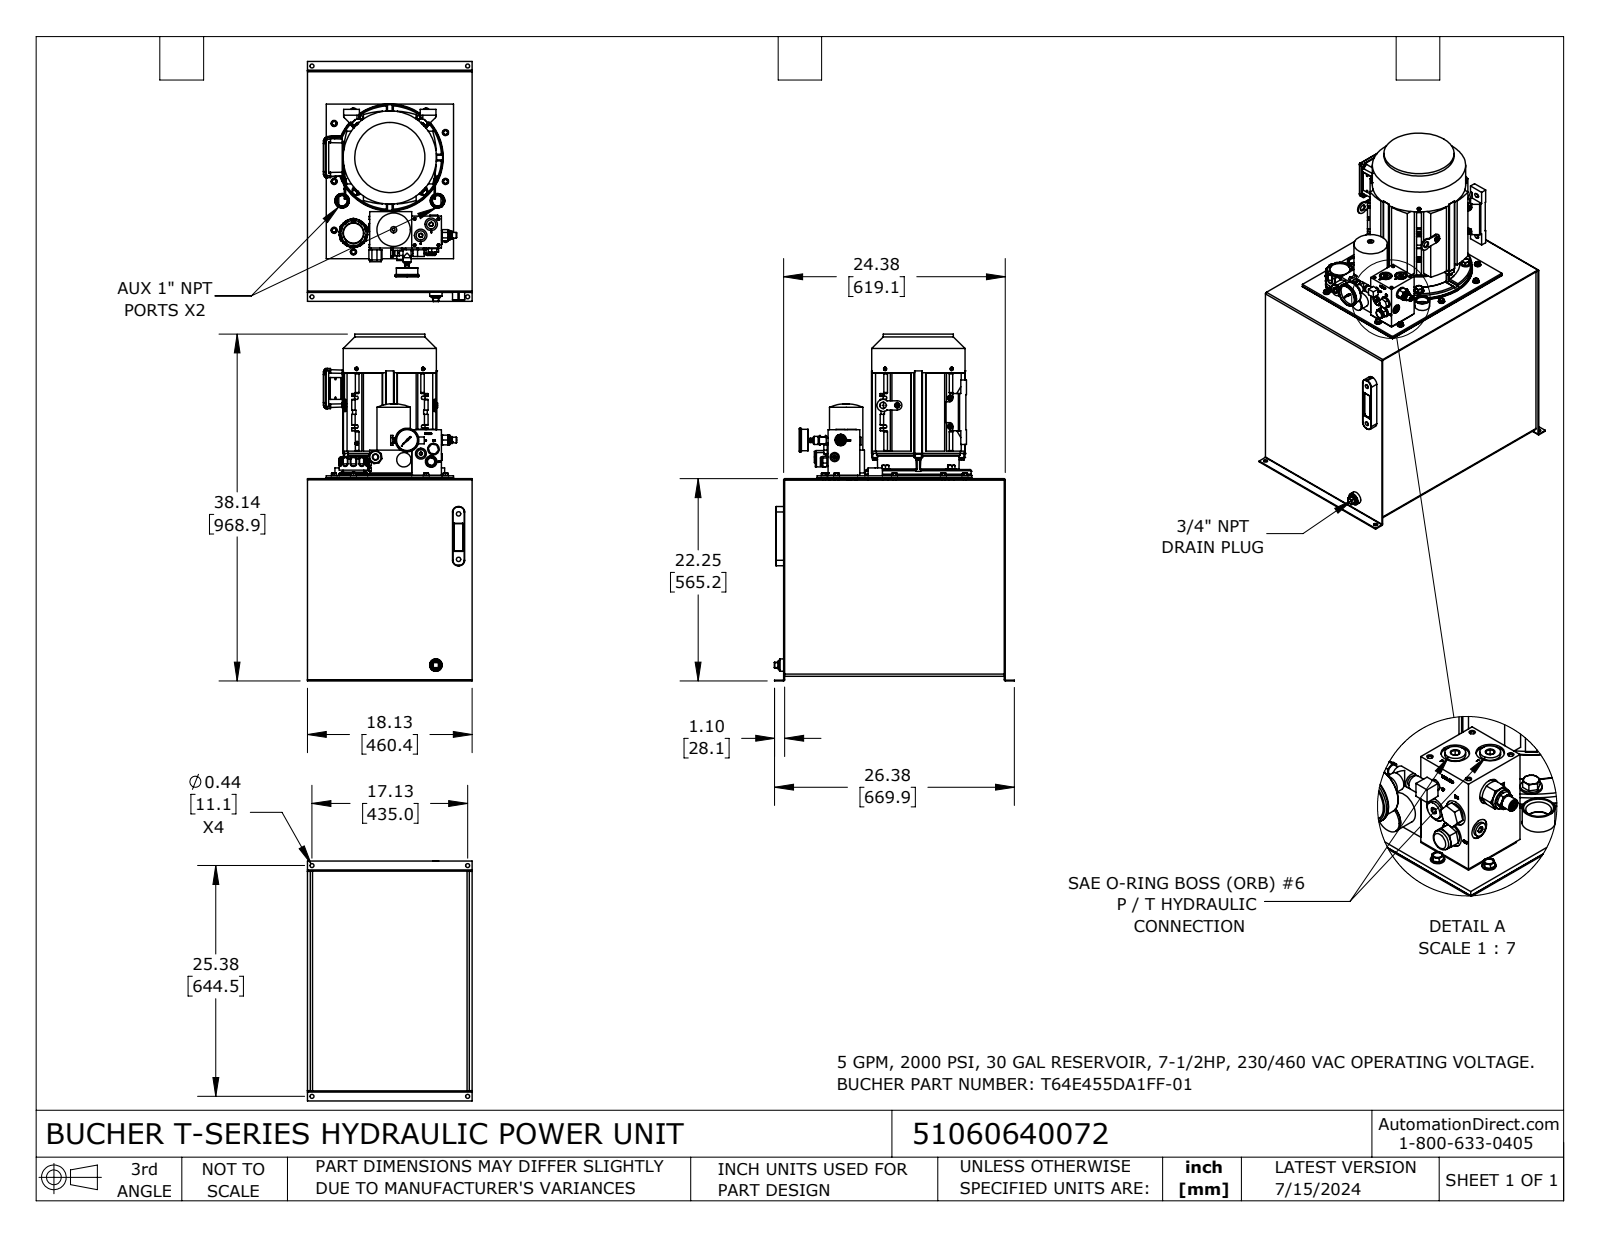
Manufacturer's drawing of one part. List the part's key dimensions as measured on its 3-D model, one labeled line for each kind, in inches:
Part name (STEP PRODUCT): 51060640072
STEP written by: SolidWorks 2023 (CONFIG_CONTROL_DESIGN)
Units: inches
Bodies: 112 solids, 5067 faces (2486 planar, 1682 cylindrical, 899 other)
Overall size (bounding box): 38.144 × 26.4 × 18.125
Volume: 1 748 in³ · Surface area: 7 698 in²
Round holes (diameter × count): ⌀0.437 ×19, ⌀0.236 ×11, ⌀0.5 ×11, ⌀0.197 ×10, ⌀0.563 ×10, ⌀0.315 ×9, ⌀0.201 ×8, ⌀0.268 ×8, ⌀0.12 ×6, ⌀0.19 ×6, ⌀0.531 ×6, ⌀0.807 ×5
Round bosses / shafts (diameter × count): ⌀0.676 ×10, ⌀0.313 ×10, ⌀0.551 ×9, ⌀0.472 ×9, ⌀0.373 ×6, ⌀0.5 ×5, ⌀0.25 ×5, ⌀1.062 ×4
Partial cylindrical surfaces — rounded edges, fillets, slot ends (radius × count): R0.02 ×188, R0.079 ×68, R0.039 ×52, R0.25 ×36, R0.063 ×20, R0.118 ×20, R0.375 ×16, R0.05 ×13
Main face-to-face distances: 0.104, 0.105, 17.395, 24.27, 21.635, 17.5, 17.291, 24.375, 24.166, 21.739
Hole centre spacings: 3.15, 3.469, 1.441, 1.442, 2.497, 6.232, 8.297, 0.78
